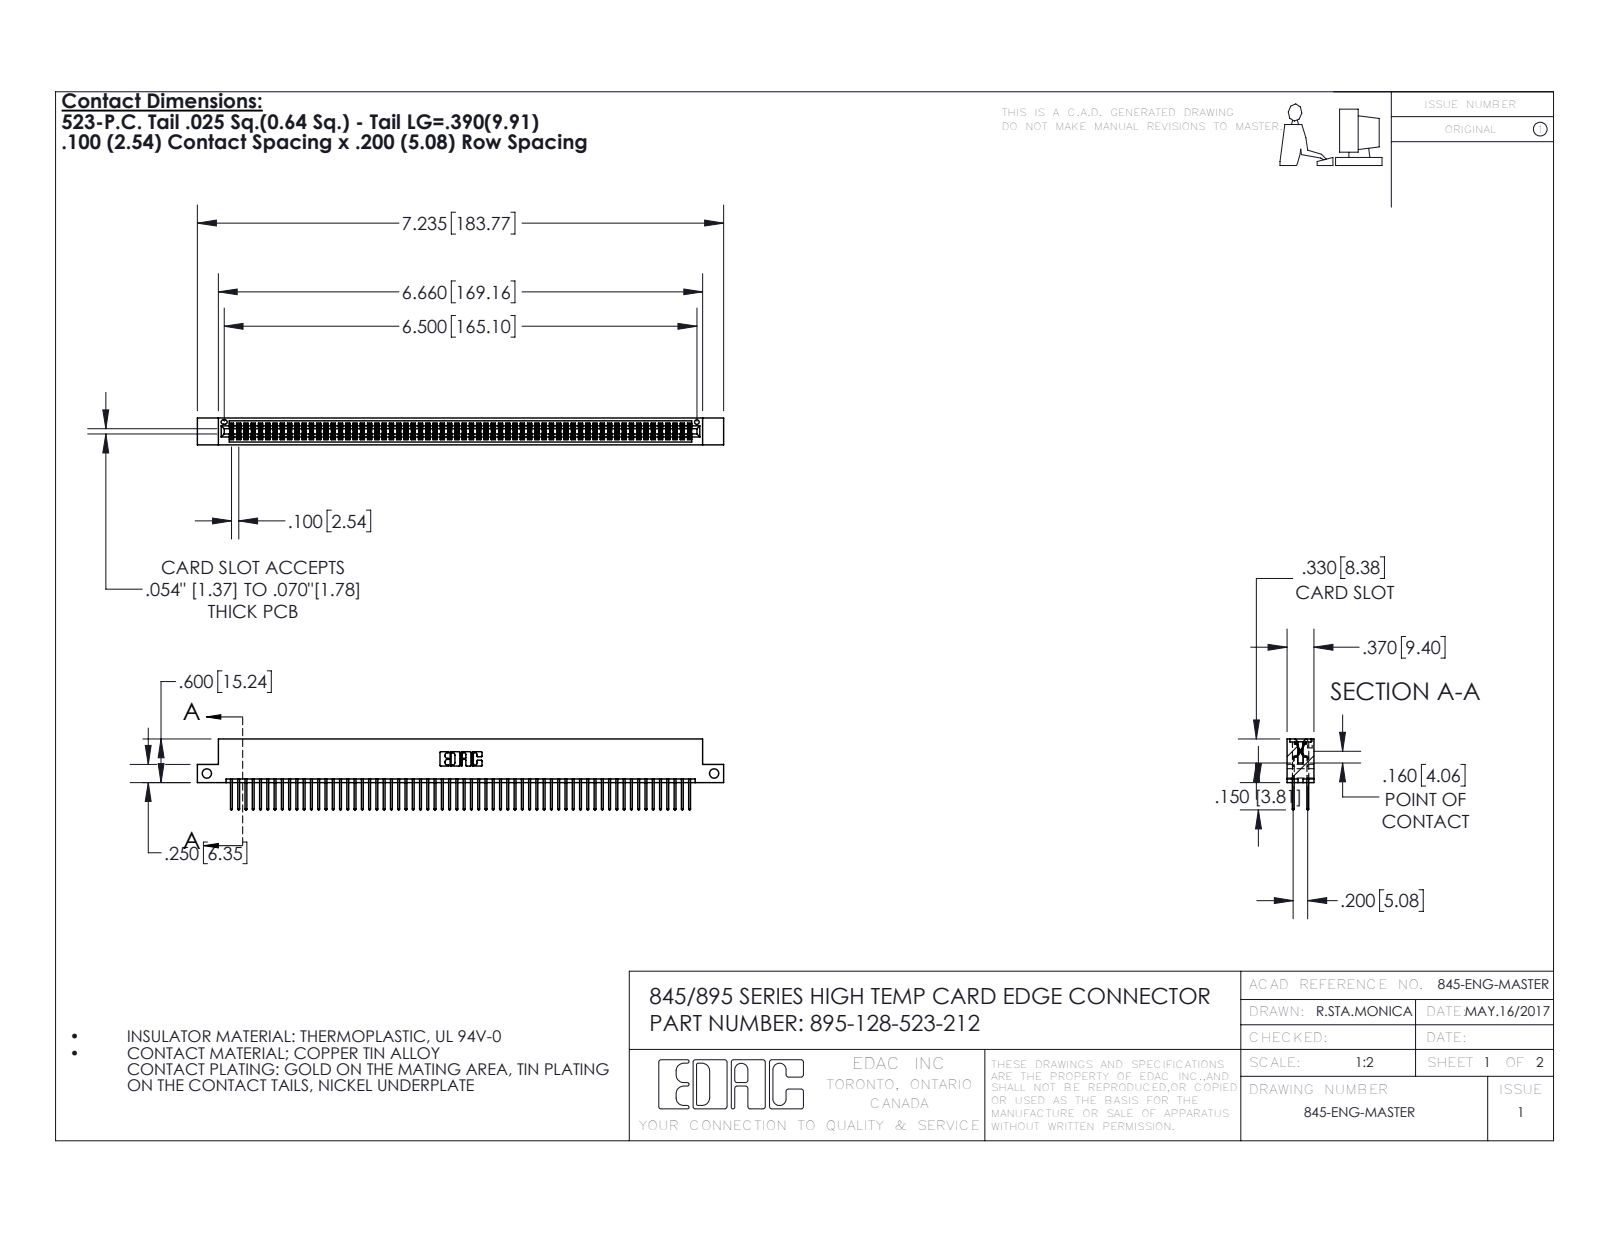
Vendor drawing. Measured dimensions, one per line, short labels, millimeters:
name: 345 Part_Flush Mounting Lugs - Side Mount; 395-128-523-212; 345-292-001_345-293-123
written by: SolidWorks 2016 (CONFIG_CONTROL_DESIGN)
unit: mm
bodies: 129 solids, 6526 faces (4304 planar, 2222 cylindrical, 0 other)
size: 183.8 × 24.8 × 9.4
volume: 18 240 mm³; area: 28 410 mm²
holes: 2× ⌀3.3, 1× ⌀1.6
rounds: 192× R0.2, 128× R0.3, 22× R0.3, 6× R0.2, 6× R0.8, 3× R0.7, 2× R0.4, 2× R0.5
face distances: 7.6, 1.8, 5.1, 2.5, 6.9, 0.6, 9.4, 5.7, 4.4, 3.8
hole spacings: 177.2
